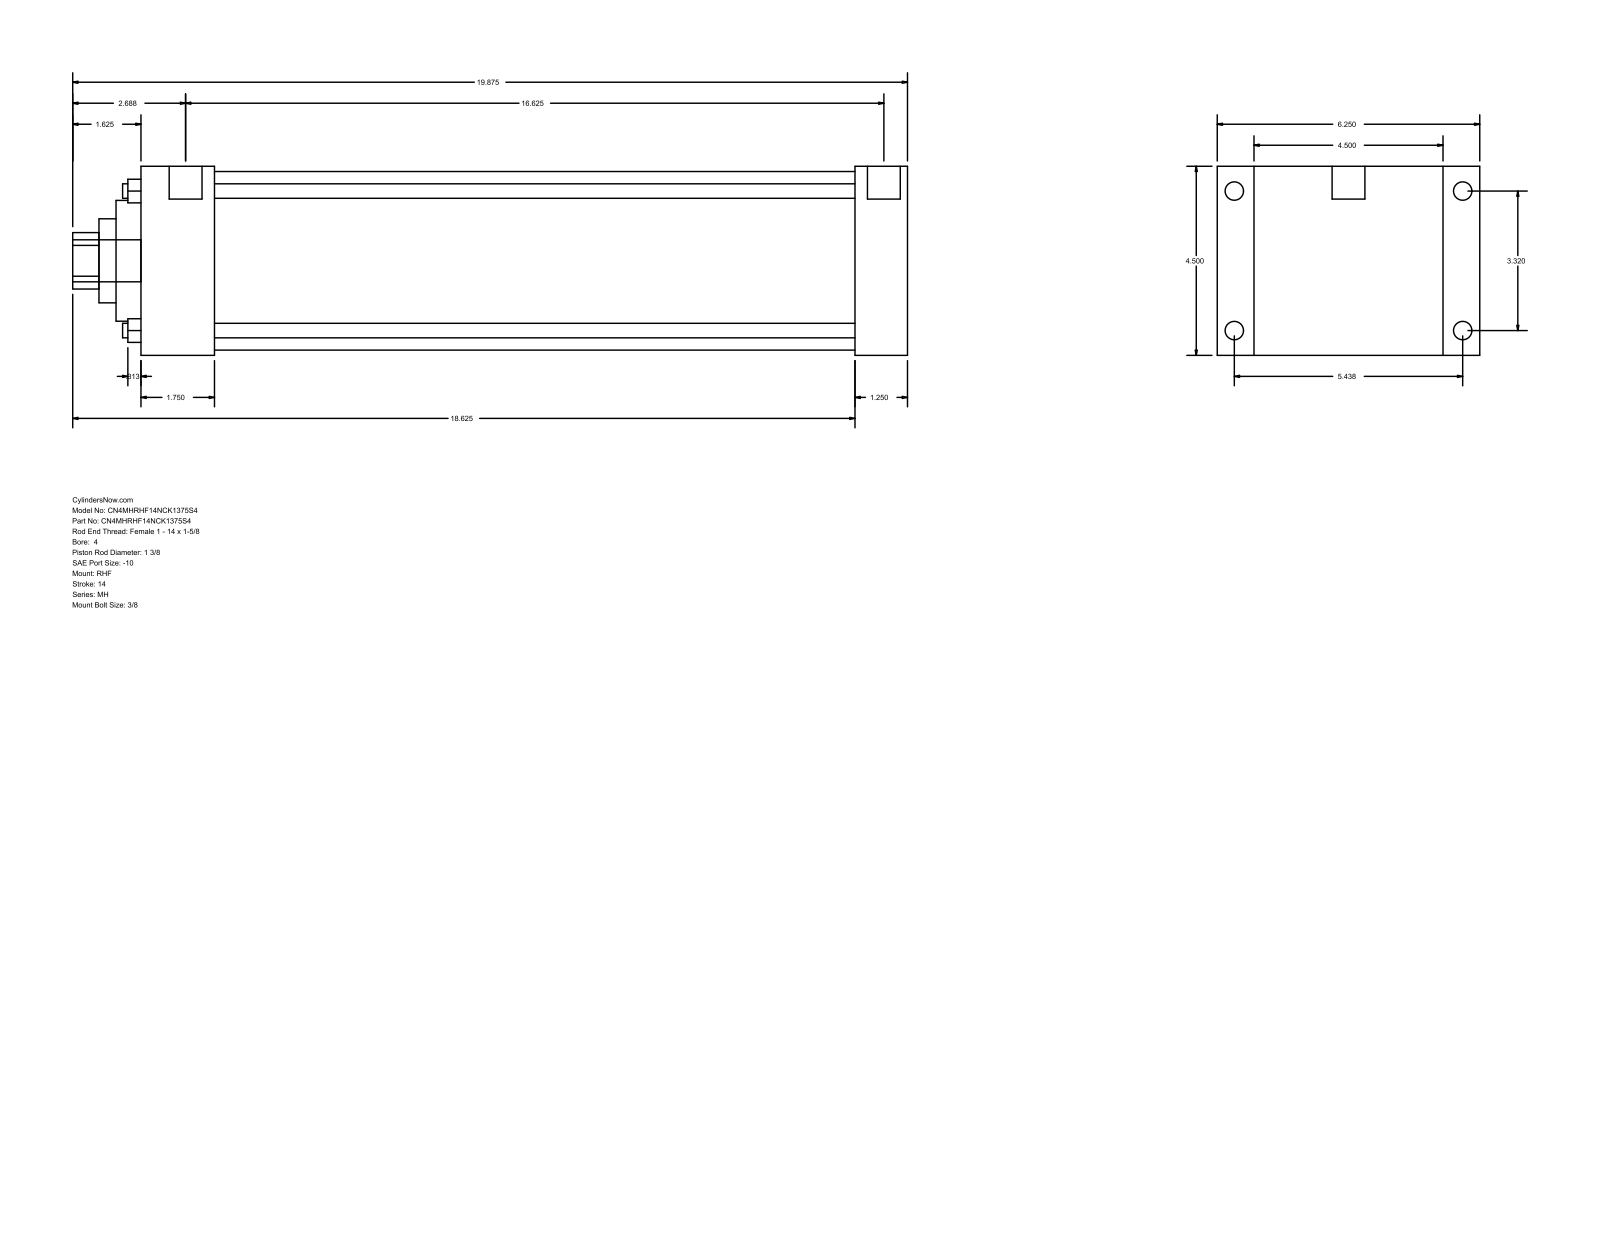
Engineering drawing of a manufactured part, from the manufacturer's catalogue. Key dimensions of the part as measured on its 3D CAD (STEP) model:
Part name (STEP PRODUCT): MH_RHF__0400_1.375
STEP written by: GSSL Pune (CONFIG_CONTROL_DESIGN)
Units: millimetres
Bodies: 0 solids, 90 faces (61 planar, 29 cylindrical, 0 other)
Overall size (bounding box): 504.82 × 158.75 × 114.3
Round holes (diameter × count): ⌀8.76 ×4, ⌀34.92 ×1, ⌀50.8 ×1, ⌀73.03 ×1, ⌀107.95 ×1
Round bosses / shafts (diameter × count): ⌀11.13 ×4, ⌀8.73 ×4, ⌀19.84 ×2, ⌀25.4 ×1
Partial cylindrical surfaces — rounded edges, fillets, slot ends (radius × count): R17.06 ×1
Main face-to-face distances: 114.3, 463.55, 431.8, 31.75, 22.23, 136.53, 44.45, 387.35, 419.1, 158.76
Hole centre spacings: 59.62, 84.32, 119.25
